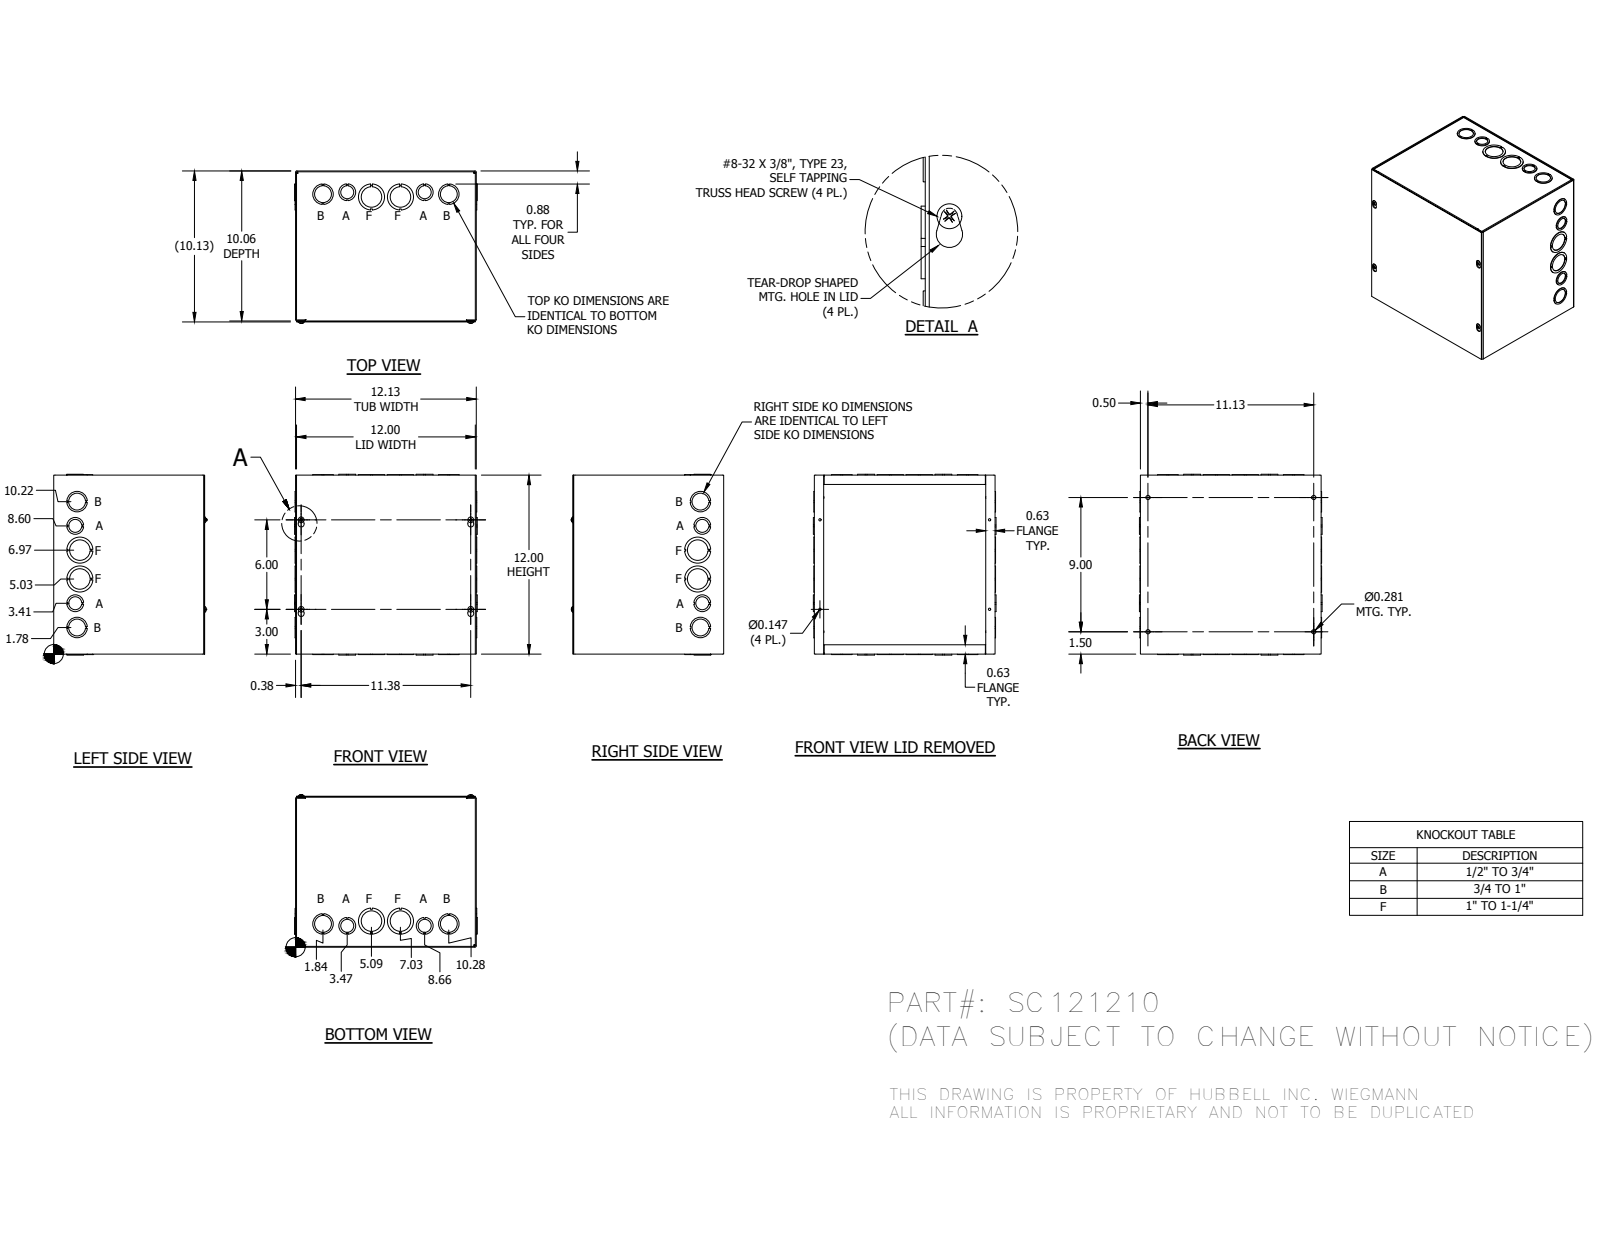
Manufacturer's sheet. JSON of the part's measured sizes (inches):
{"part_name": "SC121210BLR; SC1210TB; SC1212LPA; 34056 (+1 more)", "step_written_by": "Autodesk Inventor 2014 (AUTOMOTIVE_DESIGN)", "units": "inches", "bodies": {"solids": 21, "faces": 943, "planar": 683, "cylindrical": 192, "other": 68}, "overall_size": [12.25, 12.125, 10.225], "round_holes": [[1.125, 8], [1.375, 8], [0.147, 4], [0.281, 4], [0.875, 4], [1.75, 4]], "round_bosses_or_shafts": [[0.384, 4], [0.164, 4]], "partial_cylinders_radius": [[0.031, 12], [0.094, 12], [0.125, 4], [0.203, 4]], "face_to_face_distances": [0.063, 12, 11.937, 12.063, 10, 0.062, 10.062, 10.063, 10.125, 11.875], "hole_center_spacings": [1.505, 1.63, 1.655, 3.256, 3.579, 5.194, 6.816, 7.501]}
